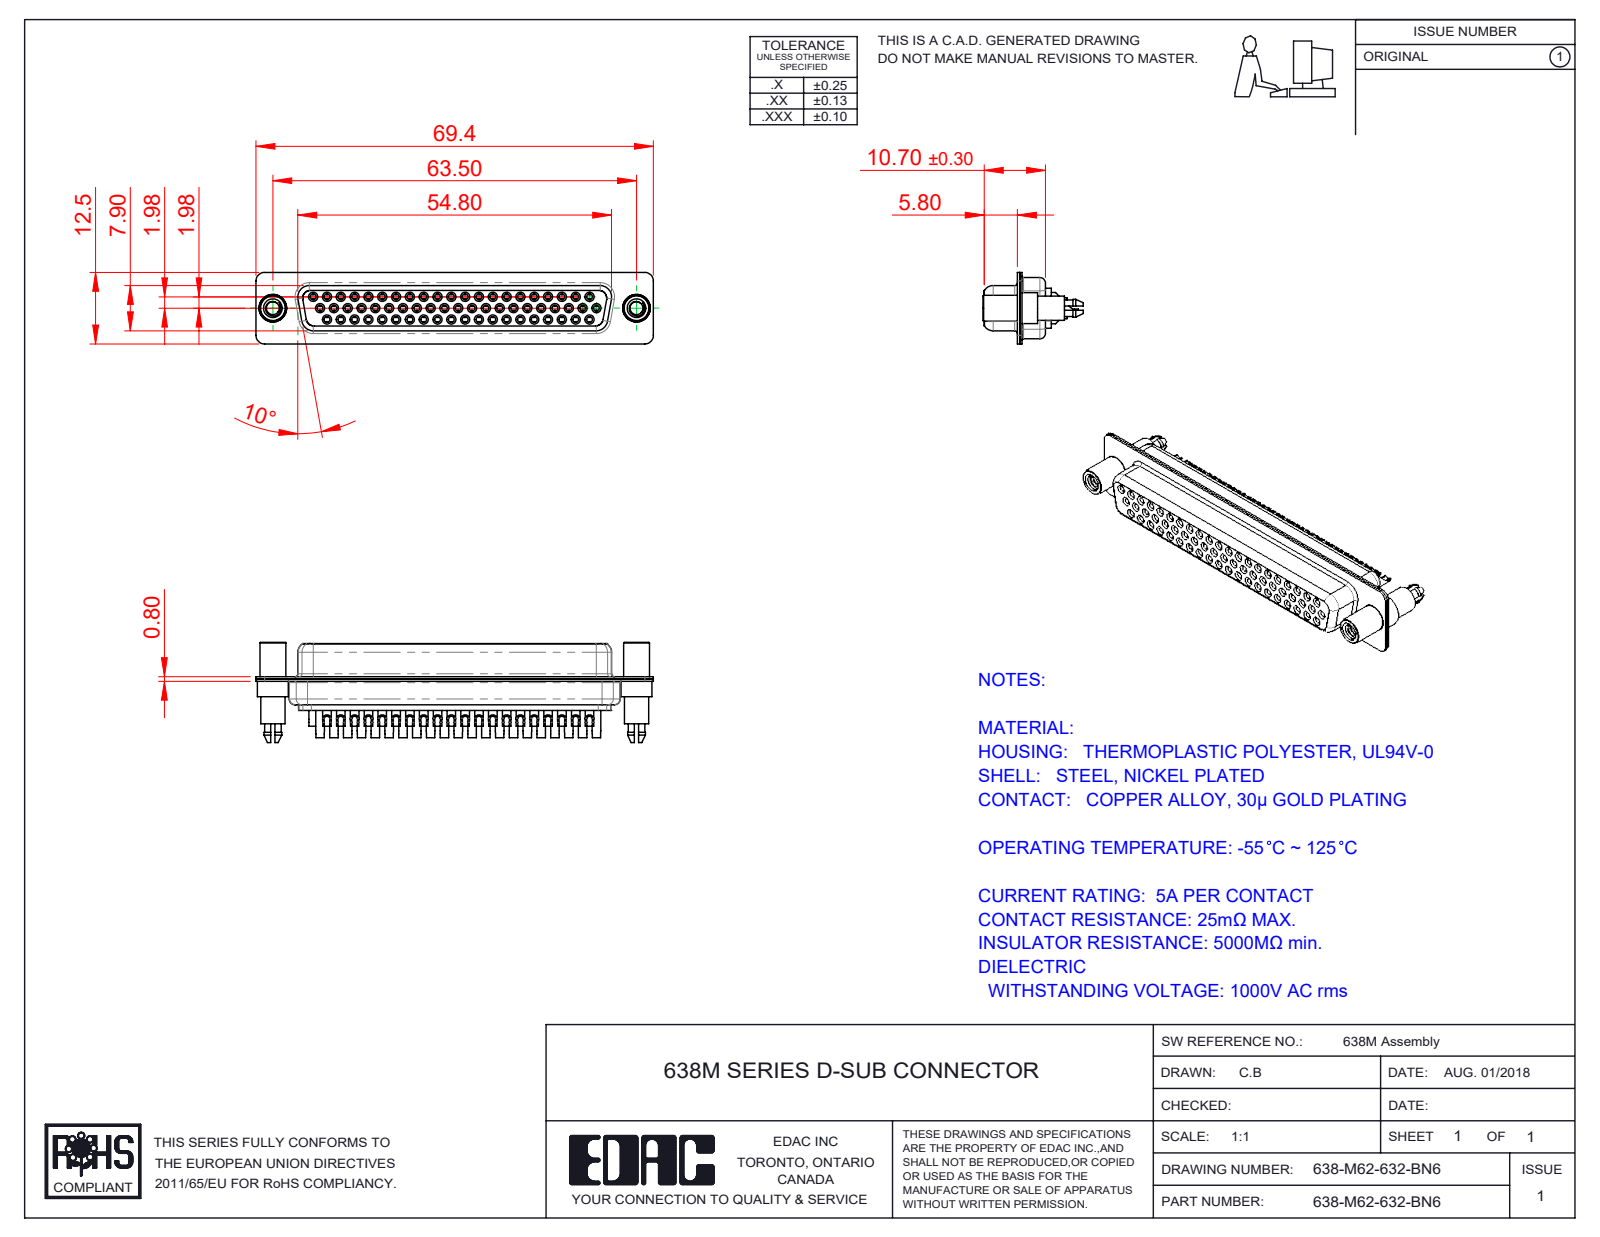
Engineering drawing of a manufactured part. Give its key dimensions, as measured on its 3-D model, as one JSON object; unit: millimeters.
{"part_name": "638M Shell Front_62 Contacts; 638M Contact Row 1_32; 638M Shell Rear_62 Contacts; 638M Contact Row 2_32 (+4 more)", "step_written_by": "SolidWorks 2020 (CONFIG_CONTROL_DESIGN)", "units": "millimeters", "bodies": {"solids": 67, "faces": 3773, "planar": 1159, "cylindrical": 1475, "other": 1139}, "overall_size": [69.4, 17.5, 12.5], "volume_mm3": 5410, "surface_area_mm2": 17359, "round_holes": [[1, 62], [1.1, 62], [1.7, 62], [1.8, 62], [2, 62], [2.26, 2], [4, 2], [4.8, 2]], "round_bosses_or_shafts": [[2.2, 62], [1.6, 62], [1.5, 62], [5.4, 2], [4.9, 2], [4.5, 2], [4.25, 2]], "partial_cylinders_radius": [[1.5, 18], [2, 12], [1.6, 10], [1.35, 8], [1, 7], [0.25, 4], [0.5, 4], [0.6, 4]], "face_to_face_distances": [0.4, 1.4, 0.45, 8.45, 8.9, 1, 1.8, 6.2, 7.05, 1.85], "hole_center_spacings": [7.24, 2.32, 2.41, 4.13, 9.65, 4.83, 14.48, 16.89]}
